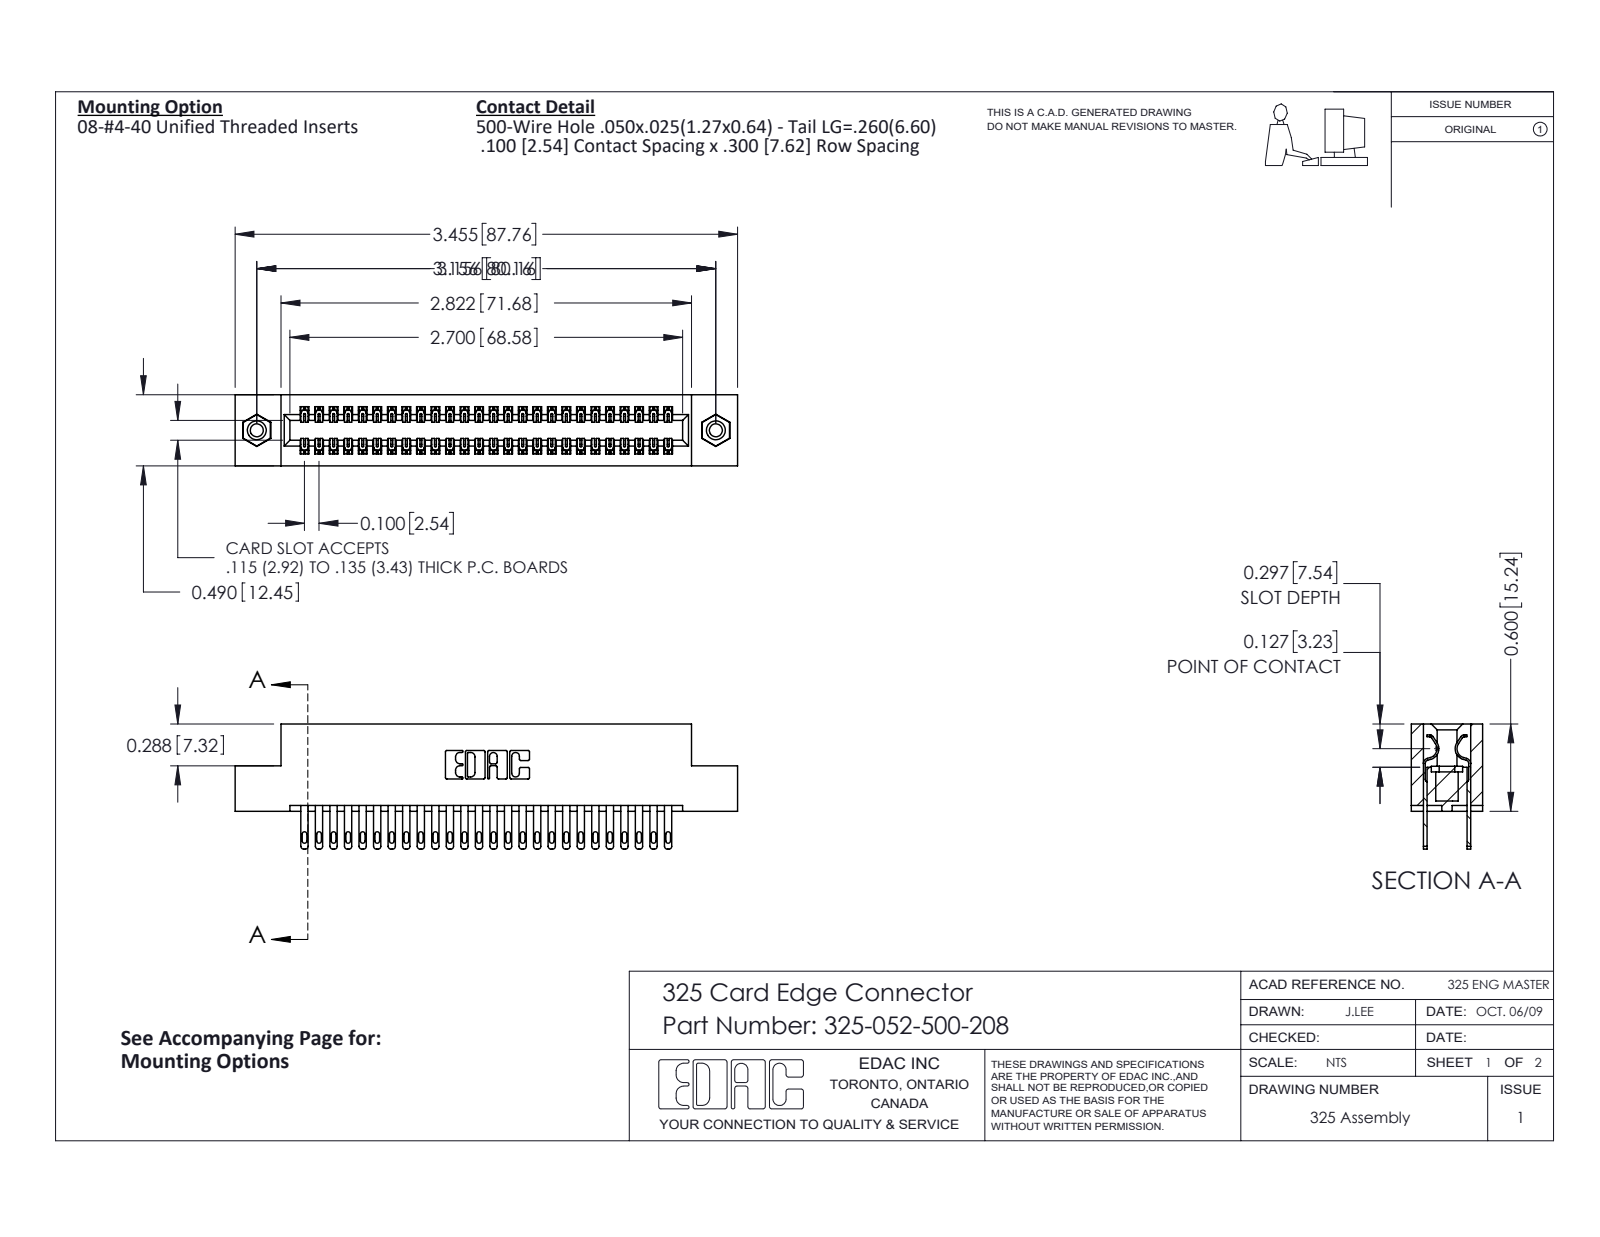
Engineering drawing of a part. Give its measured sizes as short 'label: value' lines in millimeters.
name: 345-250-001_345-250-003-102; 325-052-500-208; 325 Part_TI; 325-292-001_325-293-100
written by: SolidWorks 2016 (CONFIG_CONTROL_DESIGN)
unit: mm
bodies: 55 solids, 2670 faces (1662 planar, 992 cylindrical, 16 other)
size: 87.8 × 21.8 × 12.4
volume: 11 300 mm³; area: 13 900 mm²
holes: 2× ⌀2.3, 2× ⌀3.2, 2× ⌀4.1
bosses: 2× ⌀3.9
rounds: 78× R0.2, 52× R0.4, 52× R0.5, 22× R0.3, 6× R0.2, 6× R0.8, 3× R0.7, 2× R0.4
face distances: 2.1, 10.3, 7.6, 2.7, 9.7, 0.6, 12.4, 8.3, 7, 1
hole spacings: 80.2
